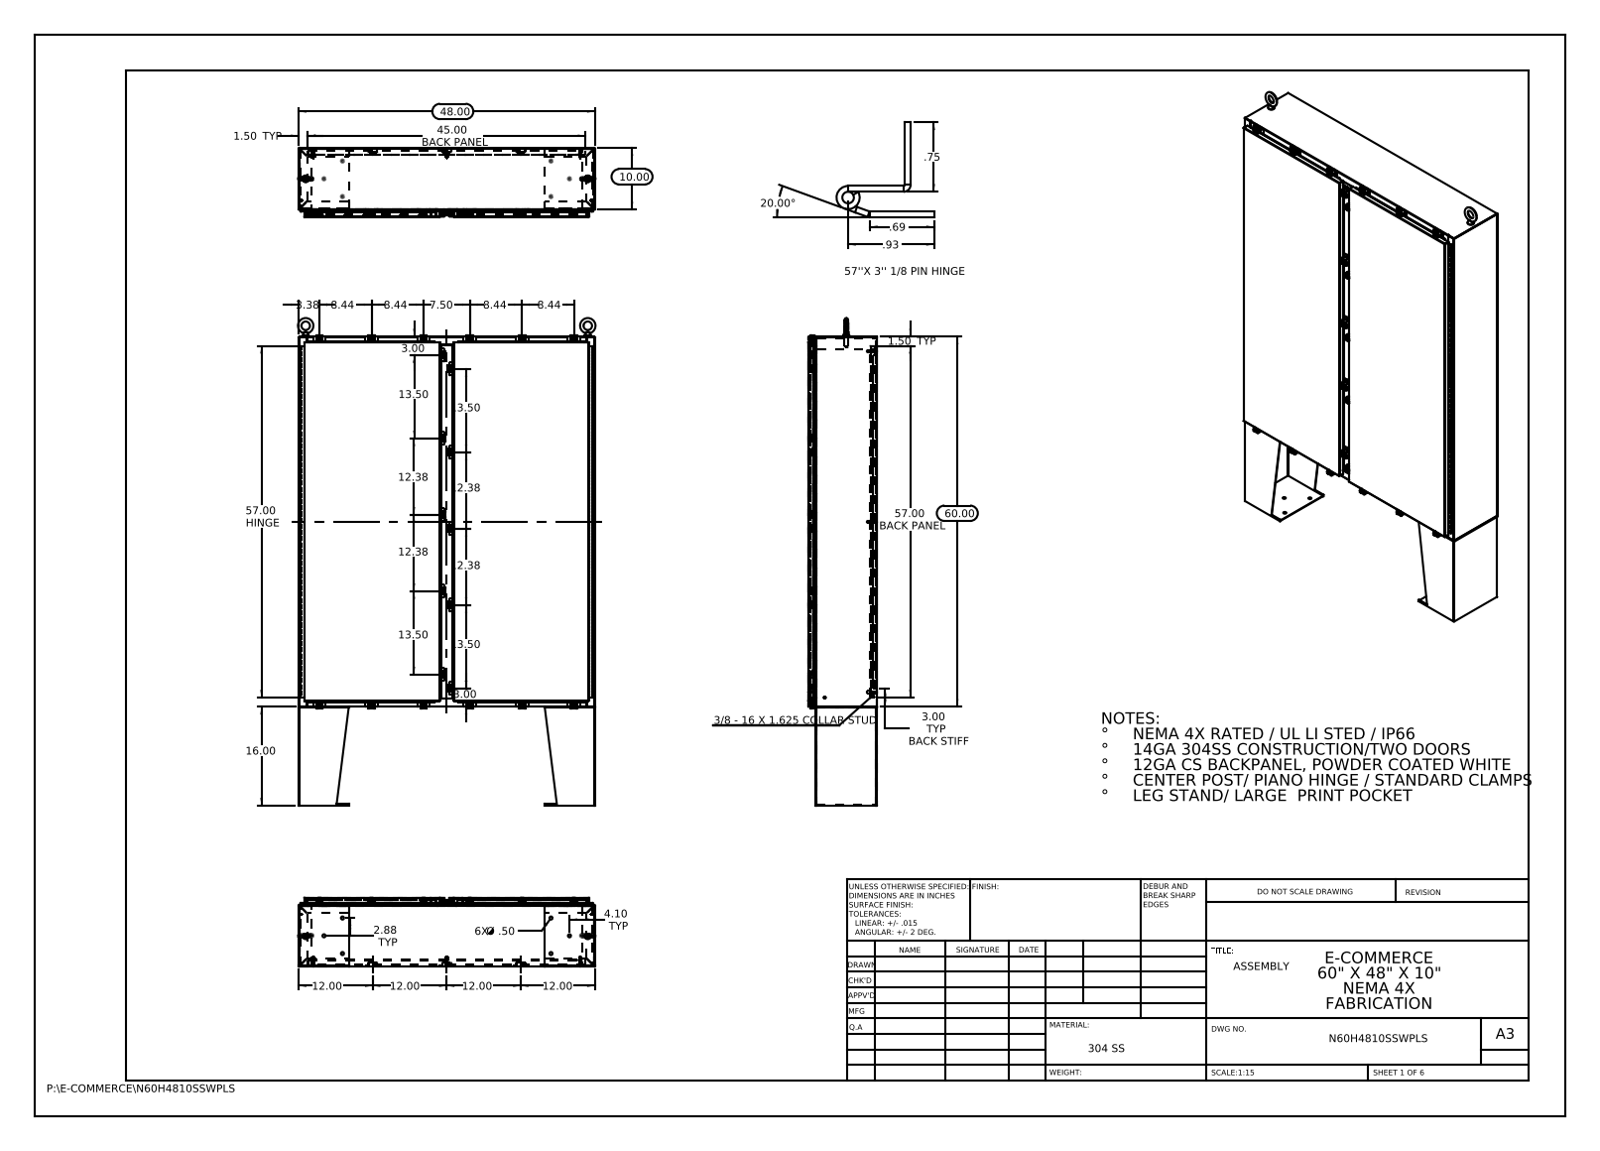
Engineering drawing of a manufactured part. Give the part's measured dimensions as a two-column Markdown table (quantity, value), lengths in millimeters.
| quantity | value |
| --- | --- |
| part name | Clamp Top; Clamp Bracket; Standard Clamps; Clamp Assembly (+8 more) |
| STEP written by | SolidWorks 2013 (CONFIG_CONTROL_DESIGN) |
| units | millimeters |
| bodies | 144 solids, 6348 faces (3306 planar, 2714 cylindrical, 328 other) |
| overall size | 2006.6 × 1224.9 × 284.5 |
| volume | 18 300 000 mm³ |
| surface area | 17 470 000 mm² |
| round holes (diameter × count) | 5.4 × 22, 6.6 × 22, 12.7 × 14, 19.1 × 4, 3.2 × 2, 3.2 × 2 |
| round bosses / shafts (diameter × count) | 6.4 × 24, 12.7 × 22, 10.1 × 22, 15.9 × 10, 9.5 × 8, 8.4 × 8, 8 × 3, 6 × 3 |
| partial cylindrical surfaces (radius × count) | 1.5 × 96, 0.3 × 48, 3 × 44, 3.6 × 44, 2.2 × 40, 1.3 × 32, 2 × 32, 2.3 × 32 |
| main face-to-face distances | 1.9, 282.6, 2.6, 27.3, 280.7, 25.4, 257.2, 29.9, 28, 255.3 |
| hole center spacings | 1524.7, 1509.5, 1631.6, 66.2, 105.6, 168.3, 168.8, 214.3 |
